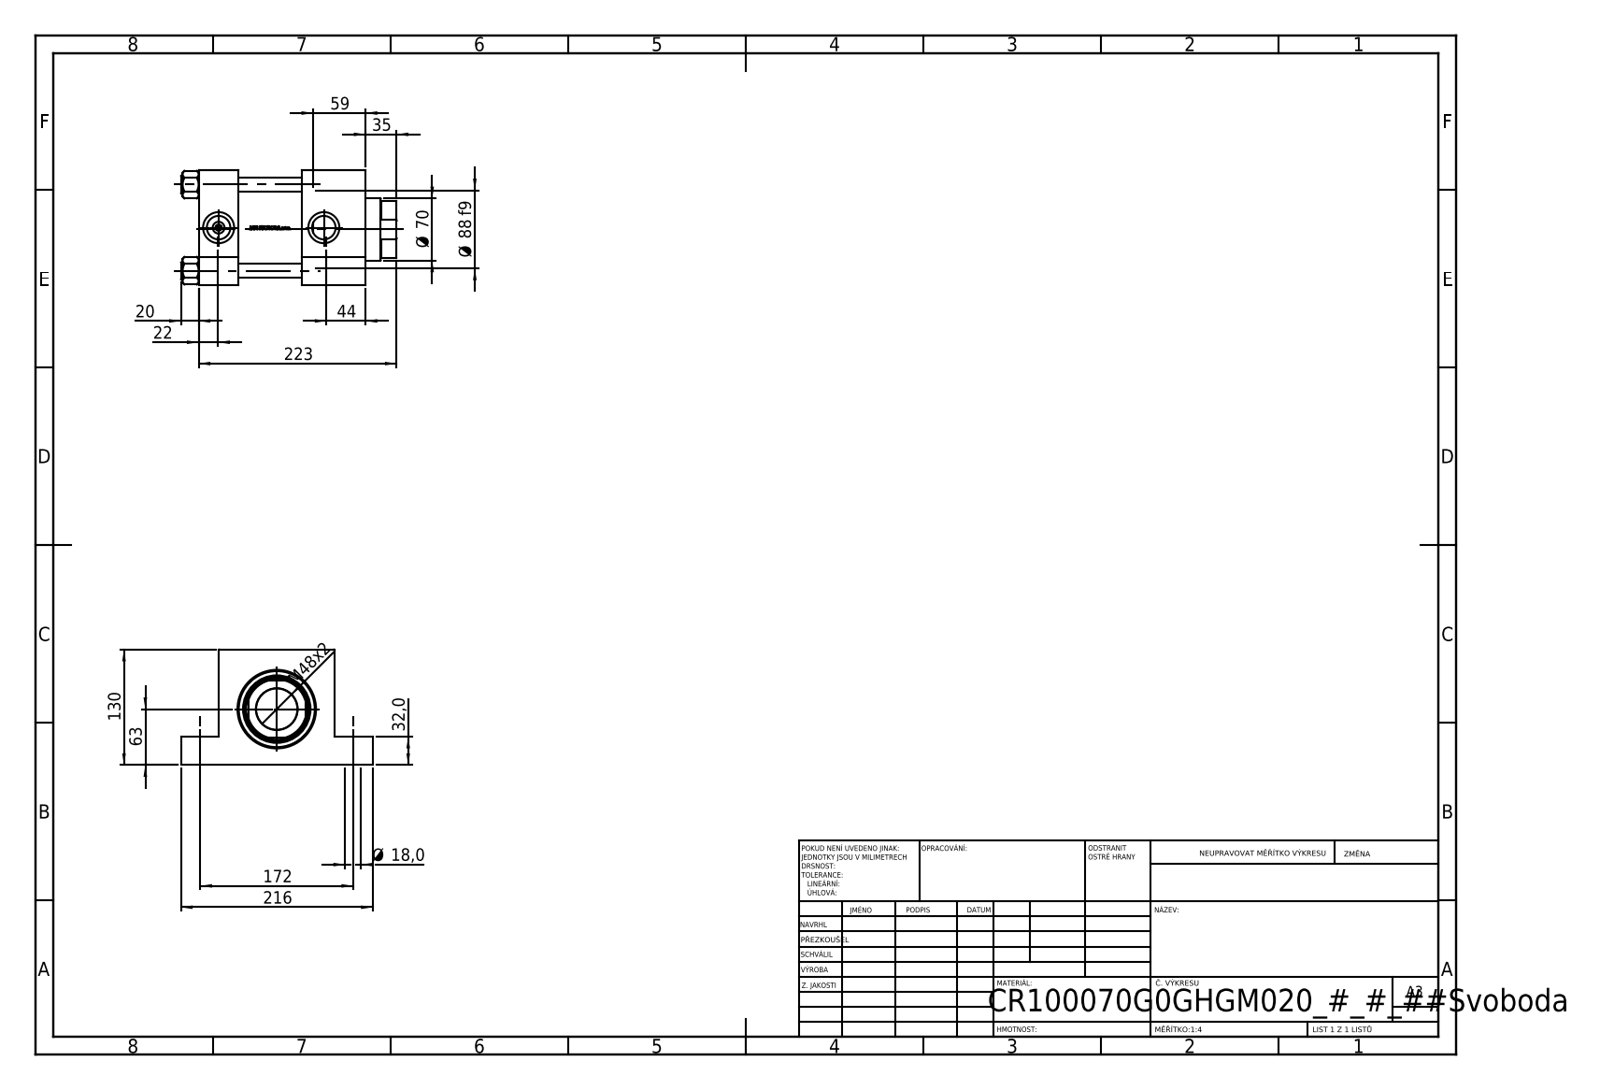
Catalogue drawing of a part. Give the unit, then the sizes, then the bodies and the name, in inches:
Units: inches
Overall size (bounding box): 9.567 × 8.504 × 5.118
Round holes (diameter × count): ⌀0.63 ×4, ⌀0.709 ×4, ⌀0.276 ×2, ⌀1.041 ×2, ⌀1.378 ×2, ⌀1.831 ×1, ⌀2.756 ×1, ⌀2.874 ×1, ⌀2.992 ×1, ⌀3.366 ×1, ⌀3.937 ×1
Round bosses / shafts (diameter × count): ⌀0.748 ×4, ⌀4.173 ×1, ⌀3.465 ×1
Partial cylindrical surfaces — rounded edges, fillets, slot ends (radius × count): R1.339 ×1
Main face-to-face distances: 5.118, 1.772, 4.567, 7.402, 5.63, 2.795, 2.835, 1.26, 3.858, 1.693
Hole centre spacings: 3.815, 2.643, 2.754, 4.803, 5.395, 6.772, 8.302, 4.665
Volume: 176.4 in³ · Surface area: 575.9 in²
Bodies: 11 solids, 1135 faces (479 planar, 124 cylindrical, 532 other)
Part name (STEP PRODUCT): V215_VC_A; V215CR_G_TYCINKA; V215CR_G_Body; NUT_M5_G (+1 more)
STEP written by: SolidWorks 2019 (CONFIG_CONTROL_DESIGN)
